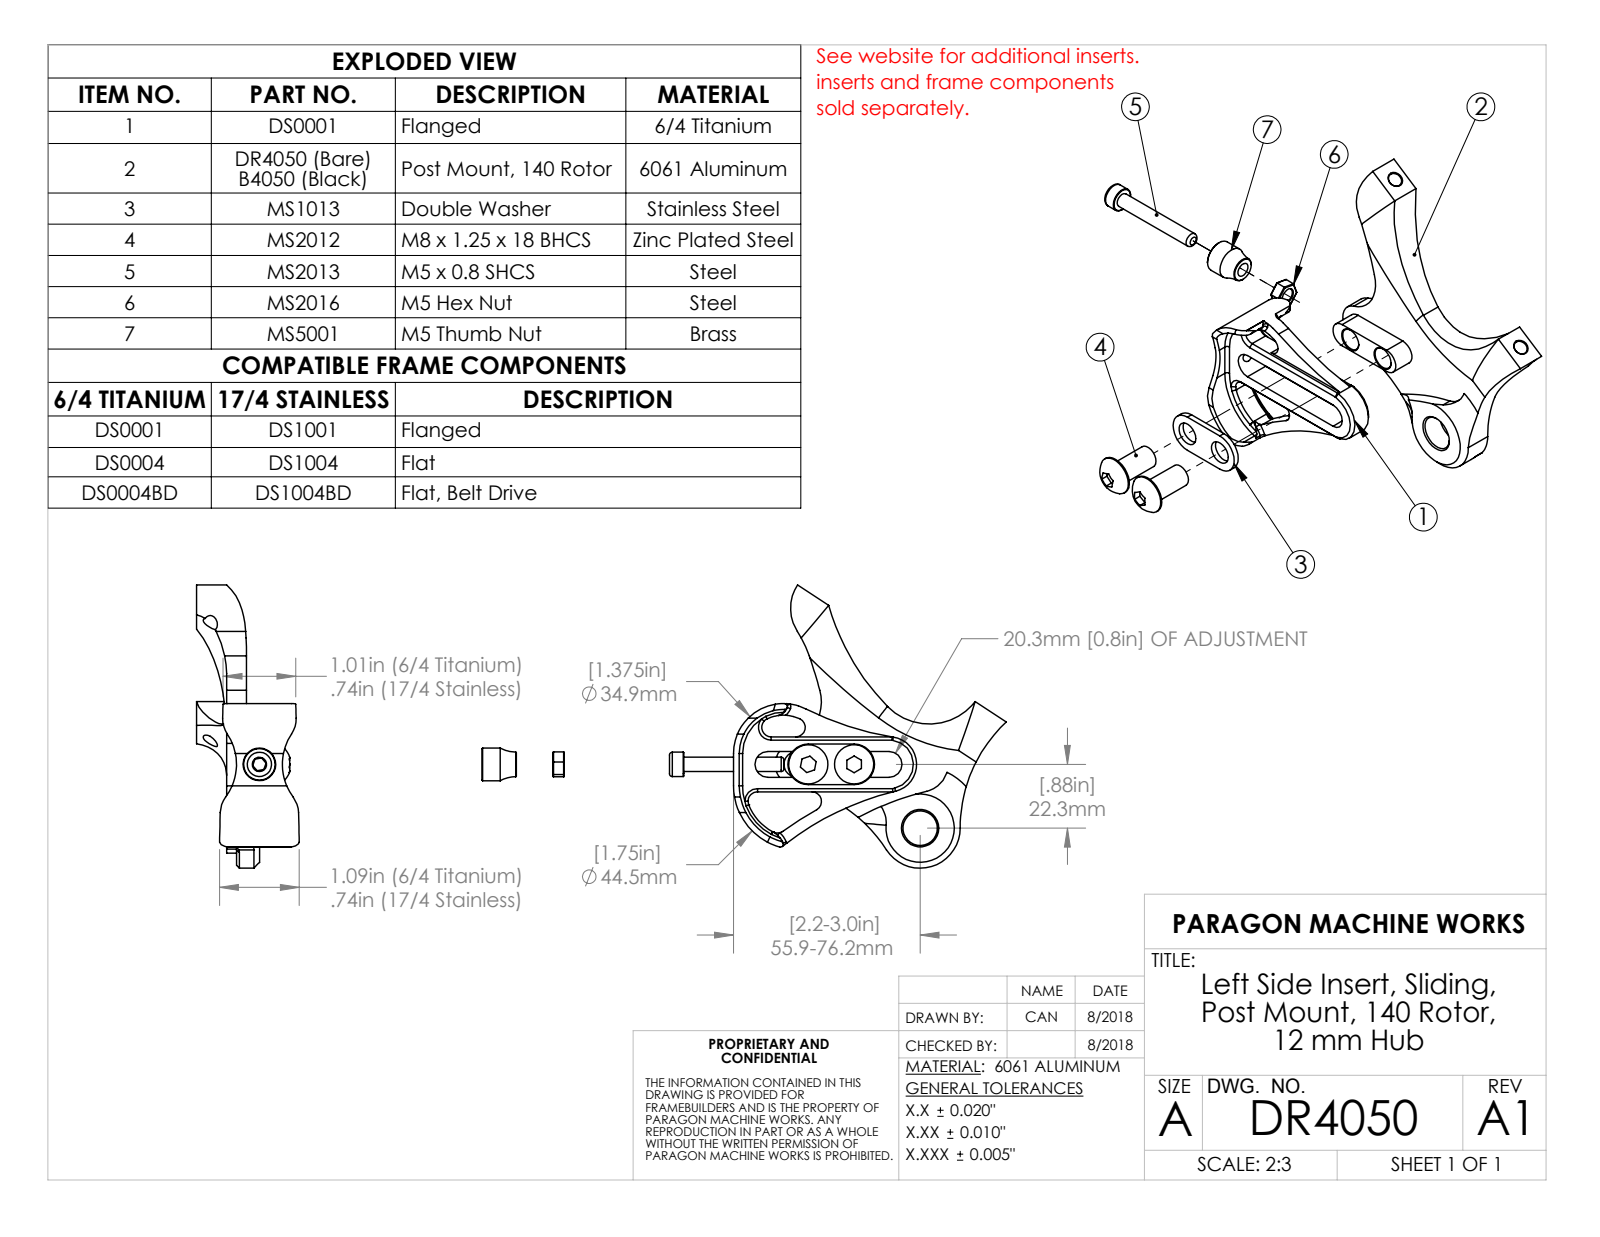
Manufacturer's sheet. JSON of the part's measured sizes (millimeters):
{"part_name": "MS5001; DR4050_Flanged; MS2013; MS2012 (+4 more)", "step_written_by": "SolidWorks 2015 (AUTOMOTIVE_DESIGN)", "units": "millimeters", "bodies": {"solids": 8, "faces": 300, "planar": 80, "cylindrical": 126, "other": 94}, "overall_size": [143, 98.9, 35.9], "volume_mm3": 42640, "surface_area_mm2": 23070, "round_holes": [[5, 3], [7.9, 2], [8.3, 2], [4.2, 1], [8.5, 1], [12, 1]], "round_bosses_or_shafts": [[13.7, 2], [8, 2], [11.4, 1]], "partial_cylinders_radius": [[0.3, 12], [3.3, 4], [4.5, 4], [9.5, 4], [1, 2], [1.1, 2], [1.2, 2], [5.1, 2]], "face_to_face_distances": [7, 2.1, 6.9, 16, 9, 9, 18, 11, 2, 12.4], "hole_center_spacings": [16, 32.1, 45, 74.2]}
